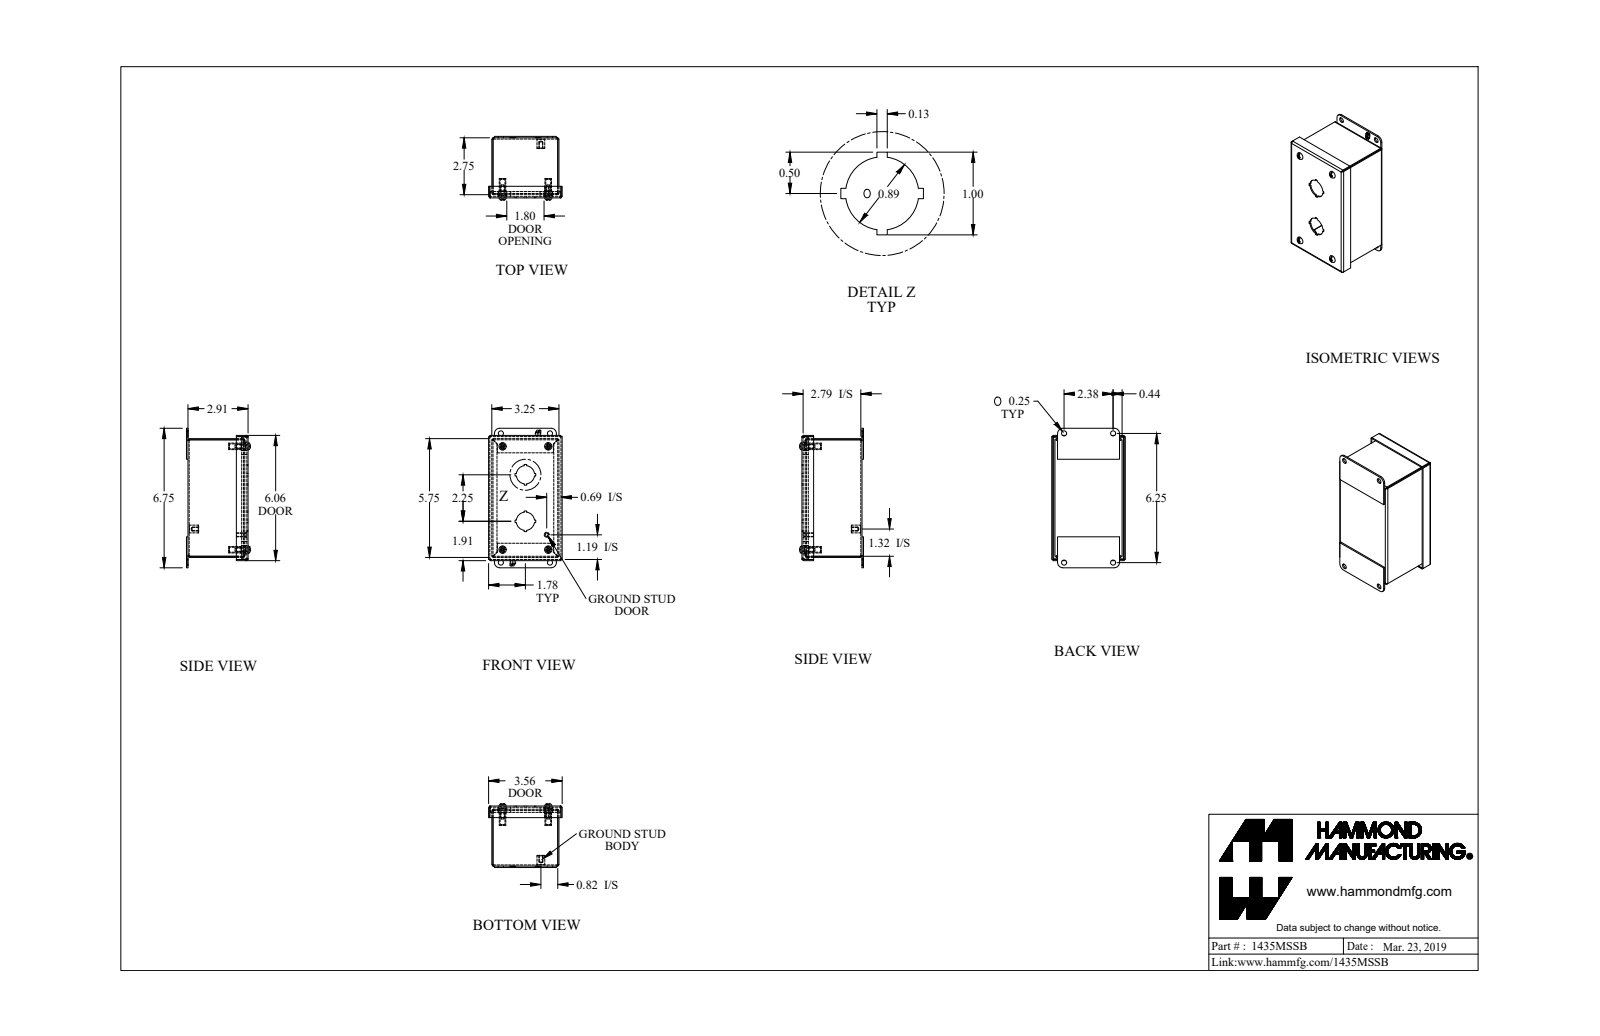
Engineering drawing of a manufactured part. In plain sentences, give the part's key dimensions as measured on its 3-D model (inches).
The part is named "1435MSSB_Default". Its 3-D file was written by "SolidWorks 2019 (CONFIG_CONTROL_DESIGN)". It is 19 solids with 477 faces: 307 planar, 140 cylindrical and 30 other. Overall it measures 6.75 by 3.562 by 3.089 inches. Its volume is 8.314 cubic inches and its surface area 257.3 square inches. Round holes: 8 of diameter 0.25, 4 of diameter 0.065, 4 of diameter 0.239, 4 of diameter 0.253, 4 of diameter 0.406, 2 of diameter 0.886, 1 of diameter 0.156. Round bosses or shafts: 5 of diameter 0.19, 4 of diameter 0.406, 4 of diameter 0.315, 4 of diameter 0.148, 1 of diameter 0.375, 1 of diameter 0.25. Partial cylindrical surfaces (rounded edges, fillets, slot ends): 12 of radius 0.029, 12 of radius 0.086, 4 of radius 0.171, 4 of radius 0.25. The main face-to-face distances are 0.057, 2.85, 0.057, 3.193, 2.907, 2.793, 5.693, 3.136, 3.25, 0.156. The hole center spacings are 5, 0.63, 0.631, 2.211, 2.376, 2.377, 5.467, 5.626.
